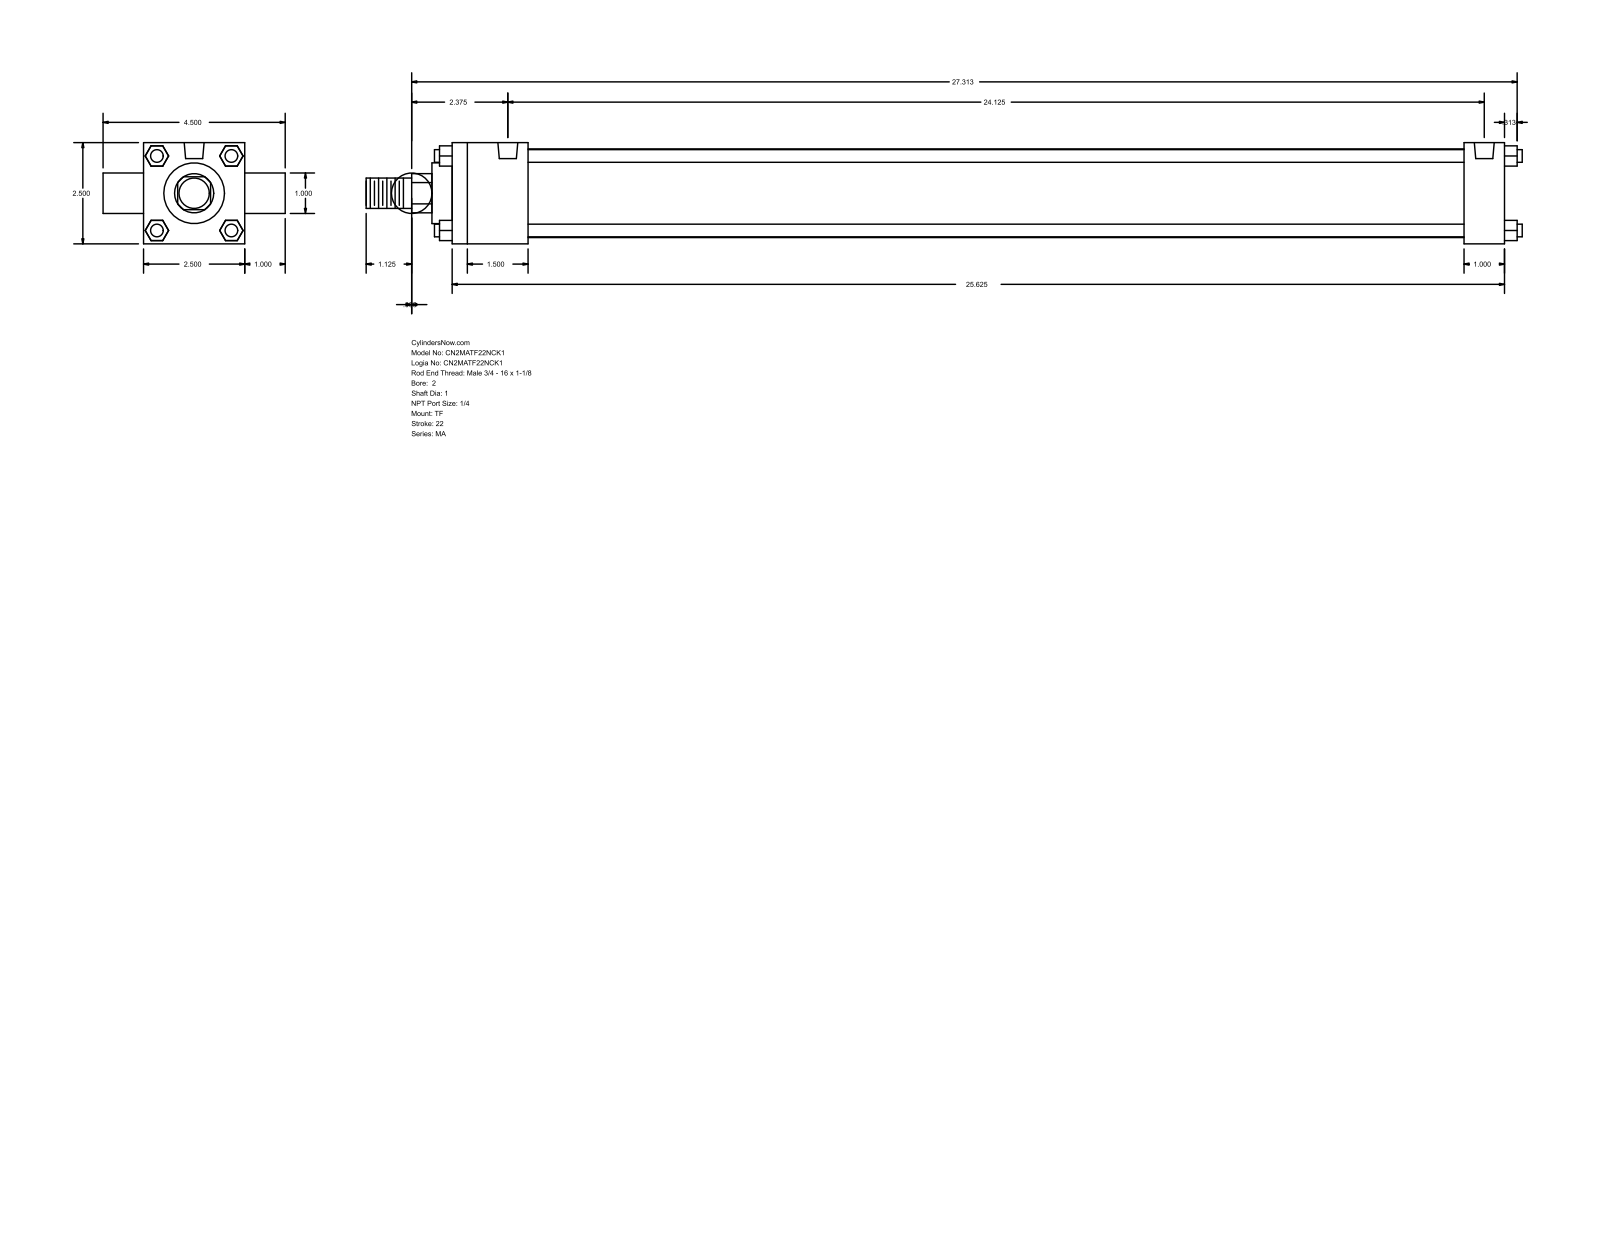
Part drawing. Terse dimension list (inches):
name: MA_TF__0200_1
written by: GSSL Pune (CONFIG_CONTROL_DESIGN)
unit: in
bodies: 0 solids, 120 faces (92 planar, 28 cylindrical, 0 other)
size: 28.563 × 4.5 × 2.5
holes: 3× ⌀0.313, 2× ⌀0.492
bosses: 4× ⌀0.313, 2× ⌀1, 1× ⌀2.19, 1× ⌀1.5, 1× ⌀0.75
rounds: 1× R0.484
face distances: 2.5, 1, 26, 0.5, 1.875, 25, 23.125, 24.125, 3.5, 0.92
hole spacings: 24.125
